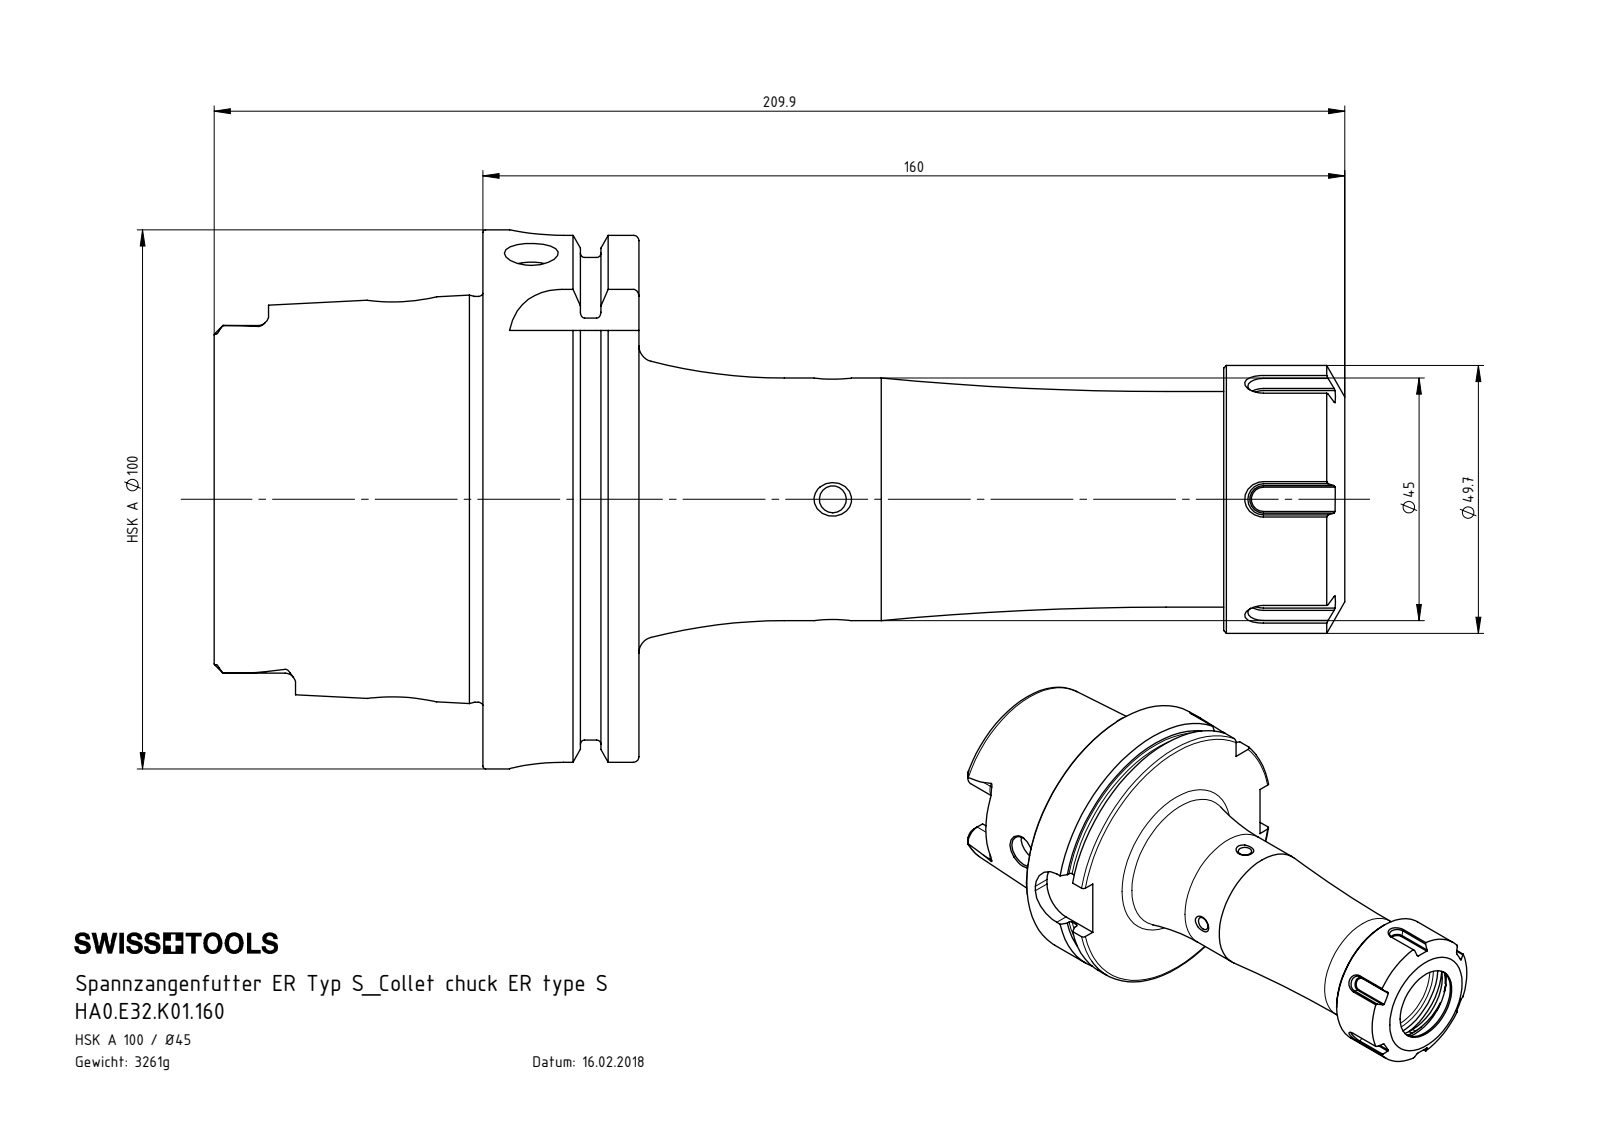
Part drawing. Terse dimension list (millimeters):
name: HA0.E32.K01.160; HA0-E32.K01.160_C_Fertigbearbeitung; ERU-AN5.K01.020_A; E32-ER1.001.022
written by: SolidWorks 2017 (CONFIG_CONTROL_DESIGN)
unit: mm
bodies: 3 solids, 339 faces (126 planar, 81 cylindrical, 132 other)
size: 209.9 × 100 × 100
volume: 415 402 mm³; area: 80 968 mm²
holes: 3× ⌀10, 2× ⌀5, 2× ⌀12, 1× ⌀6, 1× ⌀11, 1× ⌀22.5, 1× ⌀23.5, 1× ⌀26, 1× ⌀27.1, 1× ⌀38.5, 1× ⌀40.5, 1× ⌀53
bosses: 1× ⌀100, 1× ⌀91.95, 1× ⌀75.26, 1× ⌀49.7, 1× ⌀45, 1× ⌀40
rounds: 6× R1.9, 4× R4.88, 4× R10, 2× R15.5
face distances: 28.95, 12.45, 16.5, 49.9, 62.35, 78.85, 187.4, 137.5, 125.05, 108.55
hole spacings: 57.95, 79.95
